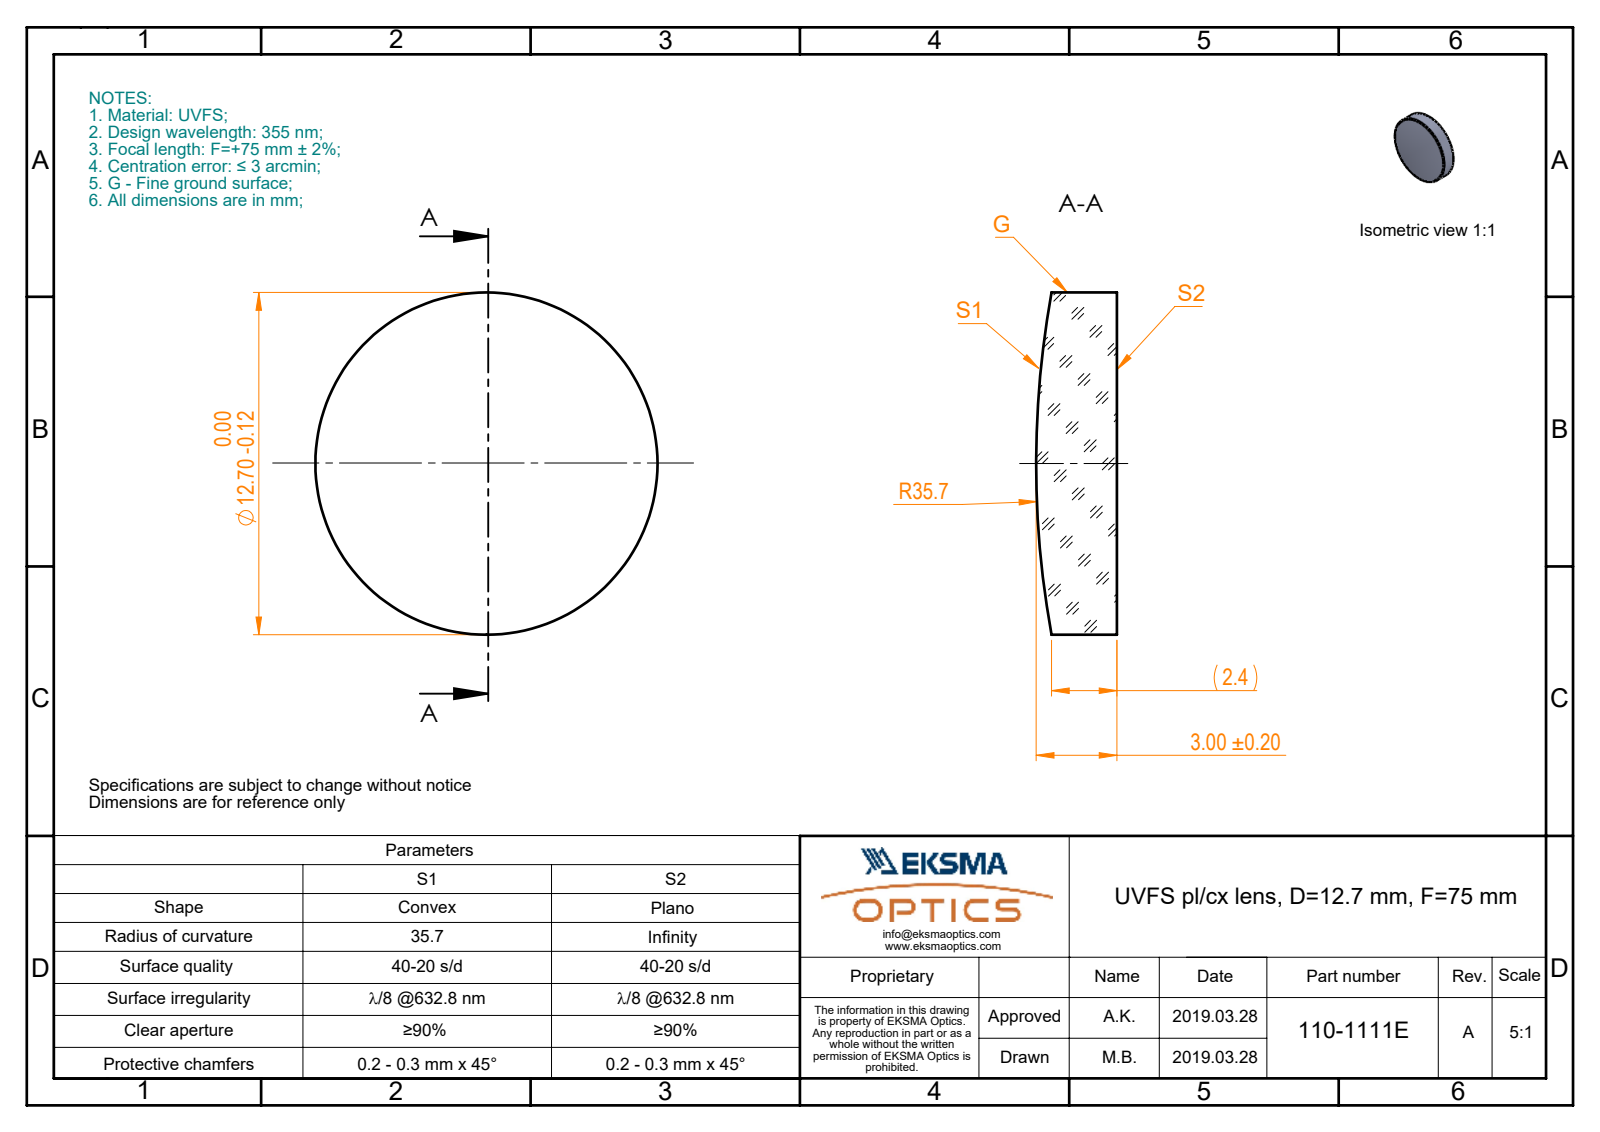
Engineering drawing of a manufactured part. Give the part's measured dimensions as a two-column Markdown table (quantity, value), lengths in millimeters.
| quantity | value |
| --- | --- |
| part name | 110-1111E UVFS pl-cx 12.7 F75 |
| STEP written by | SolidWorks 2017 (CONFIG_CONTROL_DESIGN) |
| units | millimeters |
| bodies | 1 solid, 5 faces (1 planar, 2 cylindrical, 2 other) |
| overall size | 12.7 × 12.7 × 3 |
| volume | 344 mm³ |
| surface area | 351 mm² |
| round bosses / shafts (diameter × count) | 12.7 × 1 |
